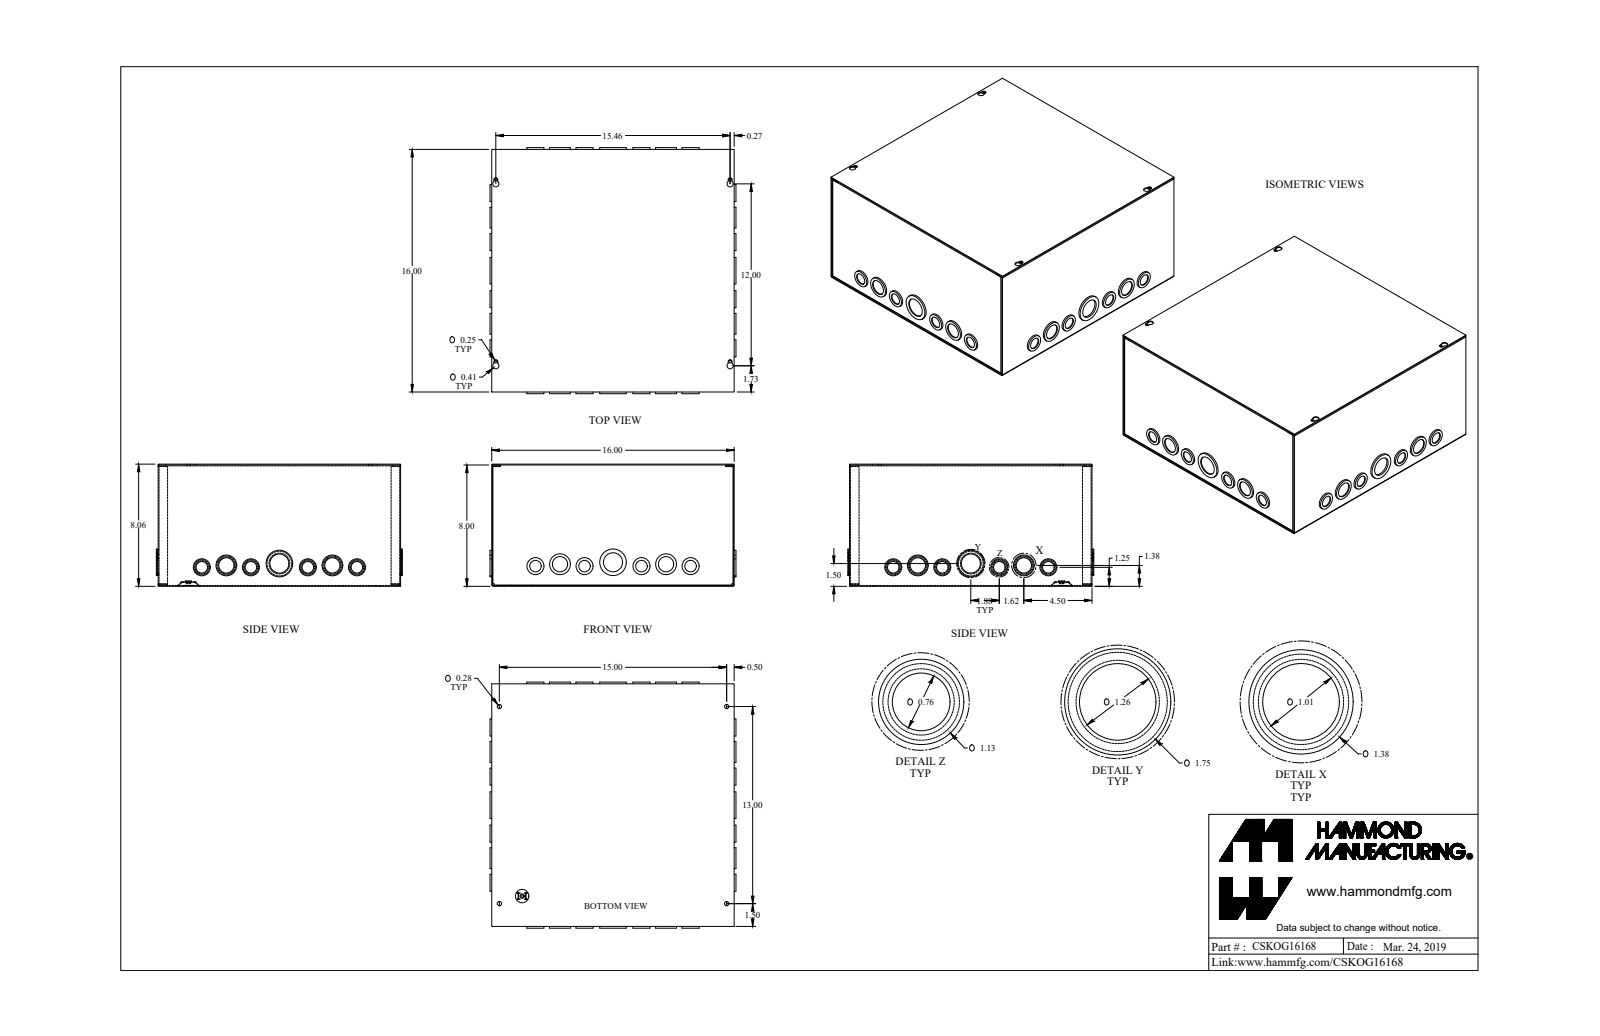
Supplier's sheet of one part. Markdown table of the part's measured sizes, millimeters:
| quantity | value |
| --- | --- |
| part name | CSKOG16168_Default |
| STEP written by | SolidWorks 2019 (CONFIG_CONTROL_DESIGN) |
| units | millimeters |
| bodies | 4 solids, 541 faces (237 planar, 296 cylindrical, 8 other) |
| overall size | 412.3 × 412.3 × 204.6 |
| volume | 1 022 000 mm³ |
| surface area | 1 421 000 mm² |
| round holes (diameter × count) | 25.7 × 12, 19.3 × 8, 32 × 6, 4.3 × 5, 7.1 × 4, 41.6 × 2, 12.7 × 1 |
| round bosses / shafts (diameter × count) | 28.6 × 10, 22.2 × 8, 22.2 × 6, 34.9 × 5, 28.6 × 4, 34.9 × 3, 44.5 × 2, 12.5 × 1 |
| partial cylindrical surfaces (radius × count) | 0.7 × 12, 2.2 × 12, 1.4 × 8, 3.2 × 4, 5.2 × 4 |
| main face-to-face distances | 1.4, 203.2, 405, 201.8, 406.4, 204.6, 403.5, 2.9, 2, 199.7 |
| hole center spacings | 41.3, 177.8, 14, 48.2, 82.3, 89, 130.2, 136.7 |
